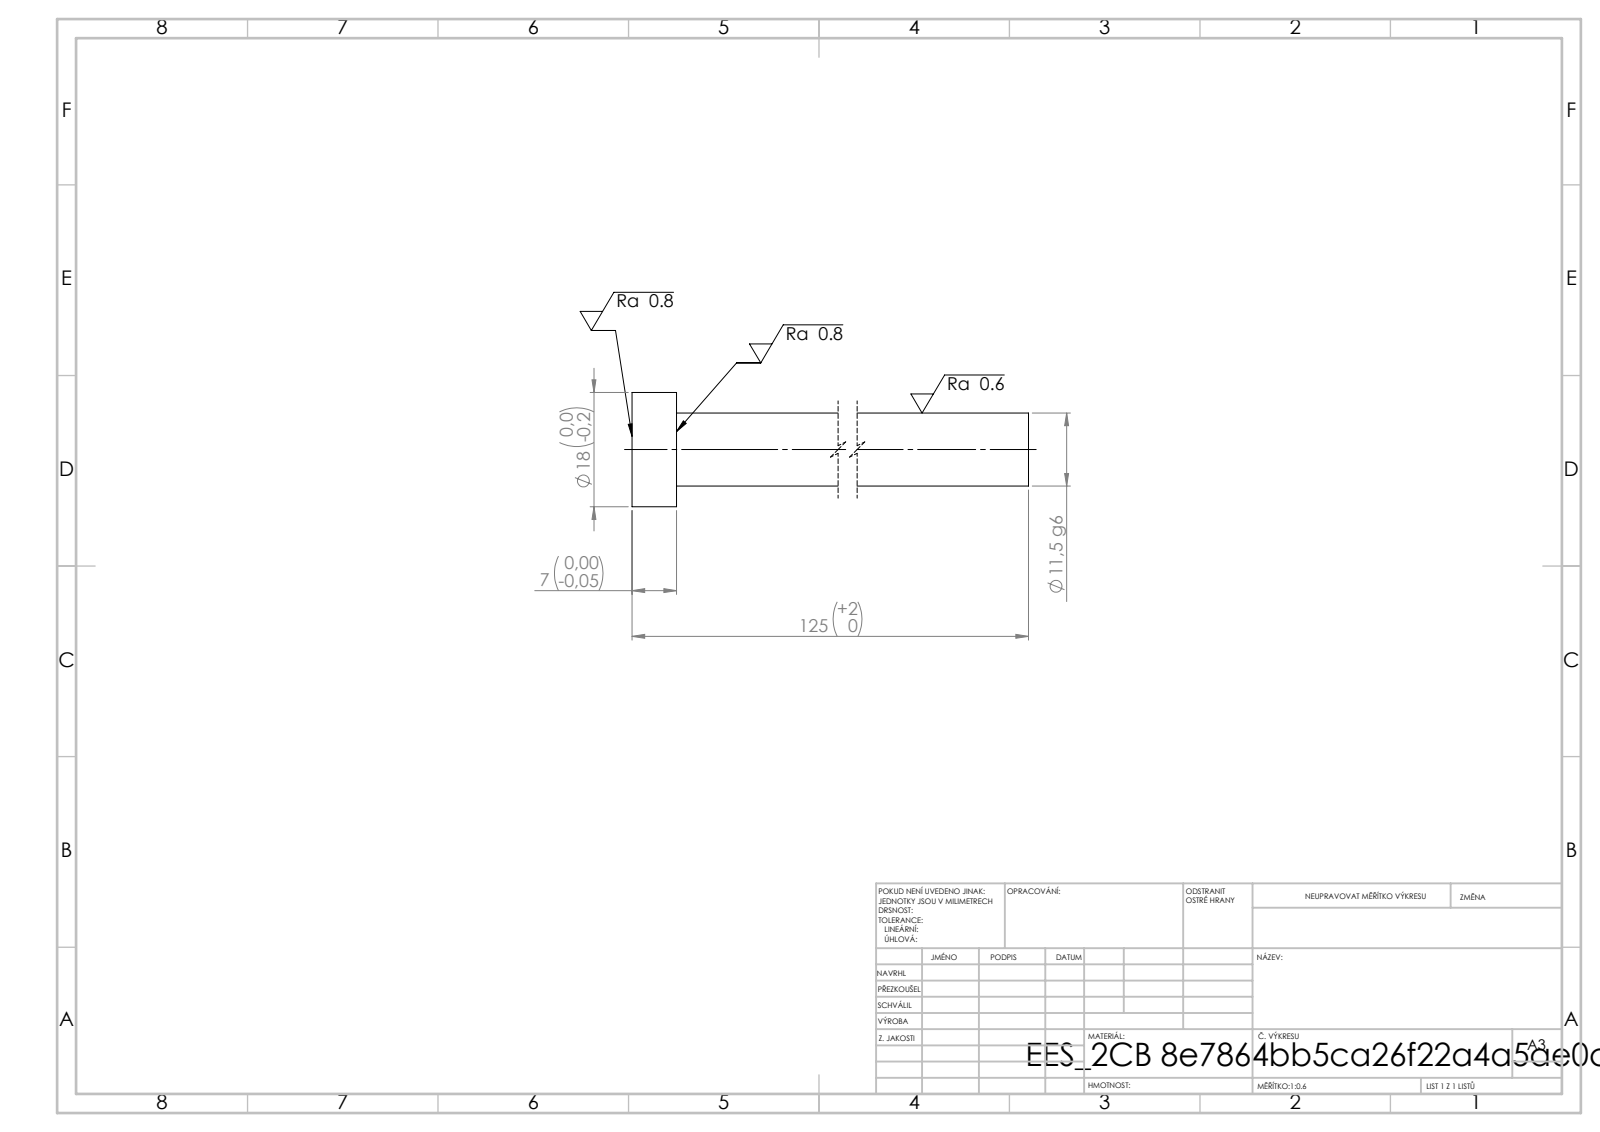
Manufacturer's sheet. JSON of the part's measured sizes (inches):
{"step_written_by": "SolidWorks 2019 (CONFIG_CONTROL_DESIGN)", "units": "inches", "bodies": {"solids": 1, "faces": 7, "planar": 3, "cylindrical": 4, "other": 0}, "overall_size": [4.921, 0.709, 0.709], "volume_in3": 0.857, "surface_area_in2": 8.01, "round_bosses_or_shafts": [[0.709, 1], [0.453, 1]], "face_to_face_distances": [0.276, 4.921, 4.646]}
